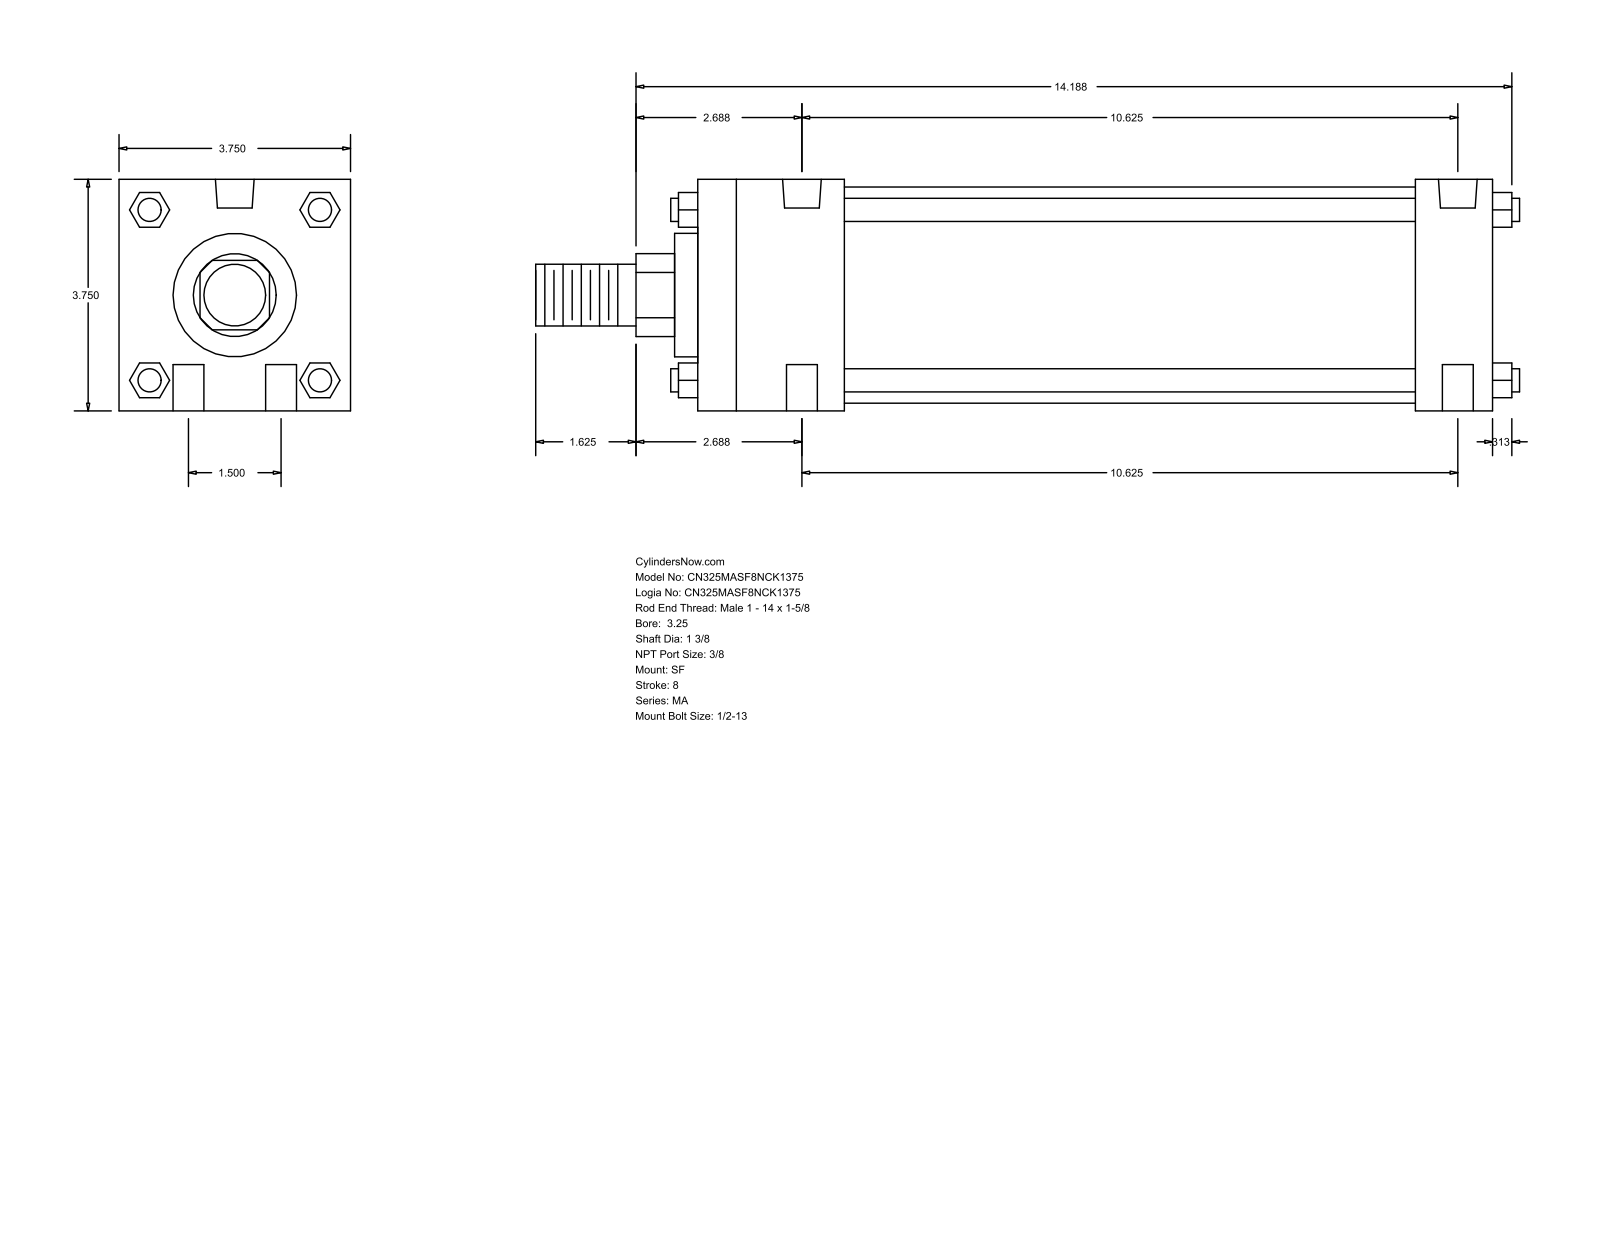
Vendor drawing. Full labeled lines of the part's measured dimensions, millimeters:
Part name (STEP PRODUCT): MA_SF__0325_1.375
STEP written by: GSSL Pune (CONFIG_CONTROL_DESIGN)
Units: millimetres
Bodies: 0 solids, 124 faces (94 planar, 30 cylindrical, 0 other)
Overall size (bounding box): 404.81 × 95.25 × 95.25
Round holes (diameter × count): ⌀12.7 ×4, ⌀11.11 ×2, ⌀15.93 ×2
Round bosses / shafts (diameter × count): ⌀9.53 ×4, ⌀88.9 ×1, ⌀50.8 ×1, ⌀34.92 ×1, ⌀25.4 ×1
Partial cylindrical surfaces — rounded edges, fillets, slot ends (radius × count): R17.06 ×1
Main face-to-face distances: 95.24, 327.03, 295.28, 31.75, 60.32, 234.96, 266.71, 9.52, 69.84, 304.8
Hole centre spacings: 19.05, 270.55, 269.88, 38.1, 272.56, 260.35
